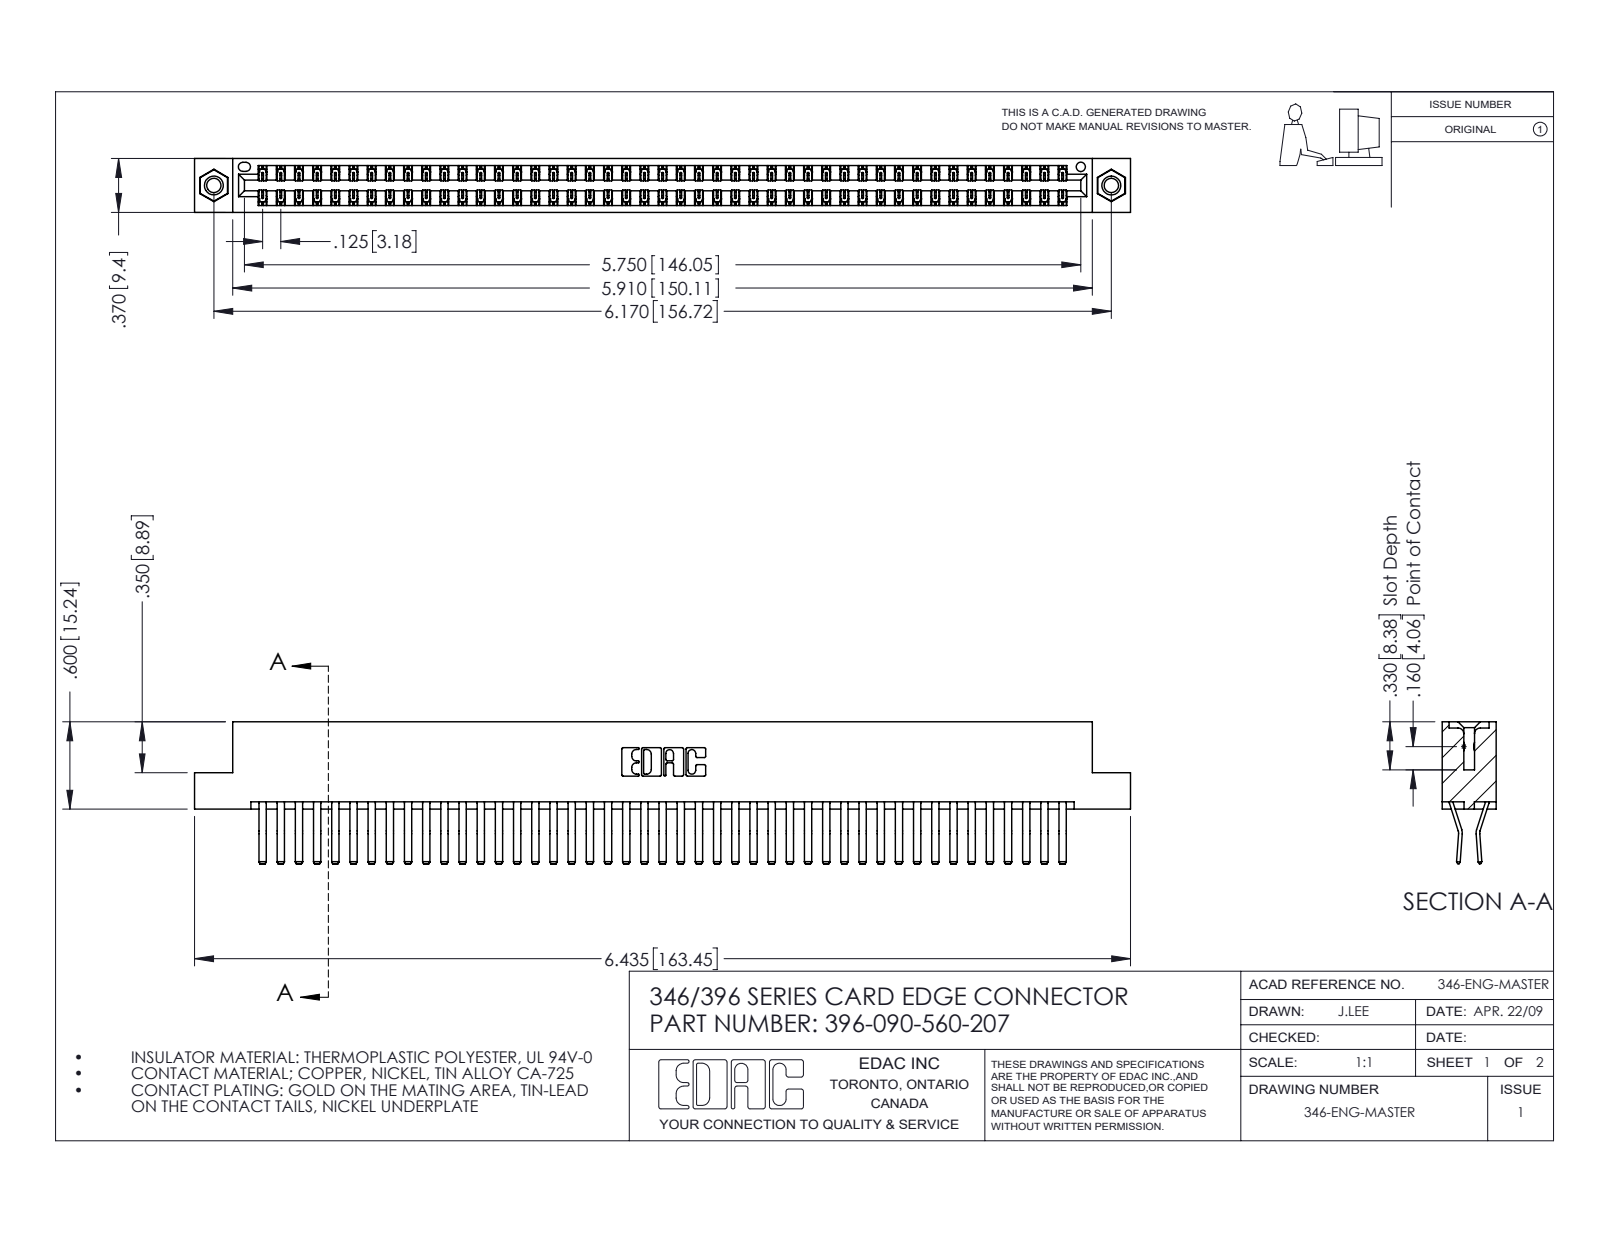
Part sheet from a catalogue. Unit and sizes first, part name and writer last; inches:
Units: inches
Overall size (bounding box): 6.435 × 0.975 × 0.37
Round holes (diameter × count): ⌀0.098 ×2, ⌀0.125 ×2, ⌀0.156 ×2, ⌀0.064 ×1
Round bosses / shafts (diameter × count): ⌀0.155 ×2
Partial cylindrical surfaces — rounded edges, fillets, slot ends (radius × count): R0.006 ×135, R0.01 ×22, R0.007 ×6, R0.031 ×6, R0.026 ×3, R0.01 ×2, R0.014 ×2, R0.022 ×2
Main face-to-face distances: 0.048, 0.322, 0.37, 0.025, 0.25, 0.072, 0.298, 0.275, 0.148, 0.222
Hole centre spacings: 0.246, 5.961, 6.17
Volume: 1.009 in³ · Surface area: 37.8 in²
Bodies: 93 solids, 5042 faces (3258 planar, 1768 cylindrical, 16 other)
Part name (STEP PRODUCT): 396-090-560-207; 345-292-001_560 Tail; 345-250-001_345-250-005-103; 346 Part_Flush Mounting Lugs - 0.156 Dia-TI
STEP written by: SolidWorks 2016 (CONFIG_CONTROL_DESIGN)
